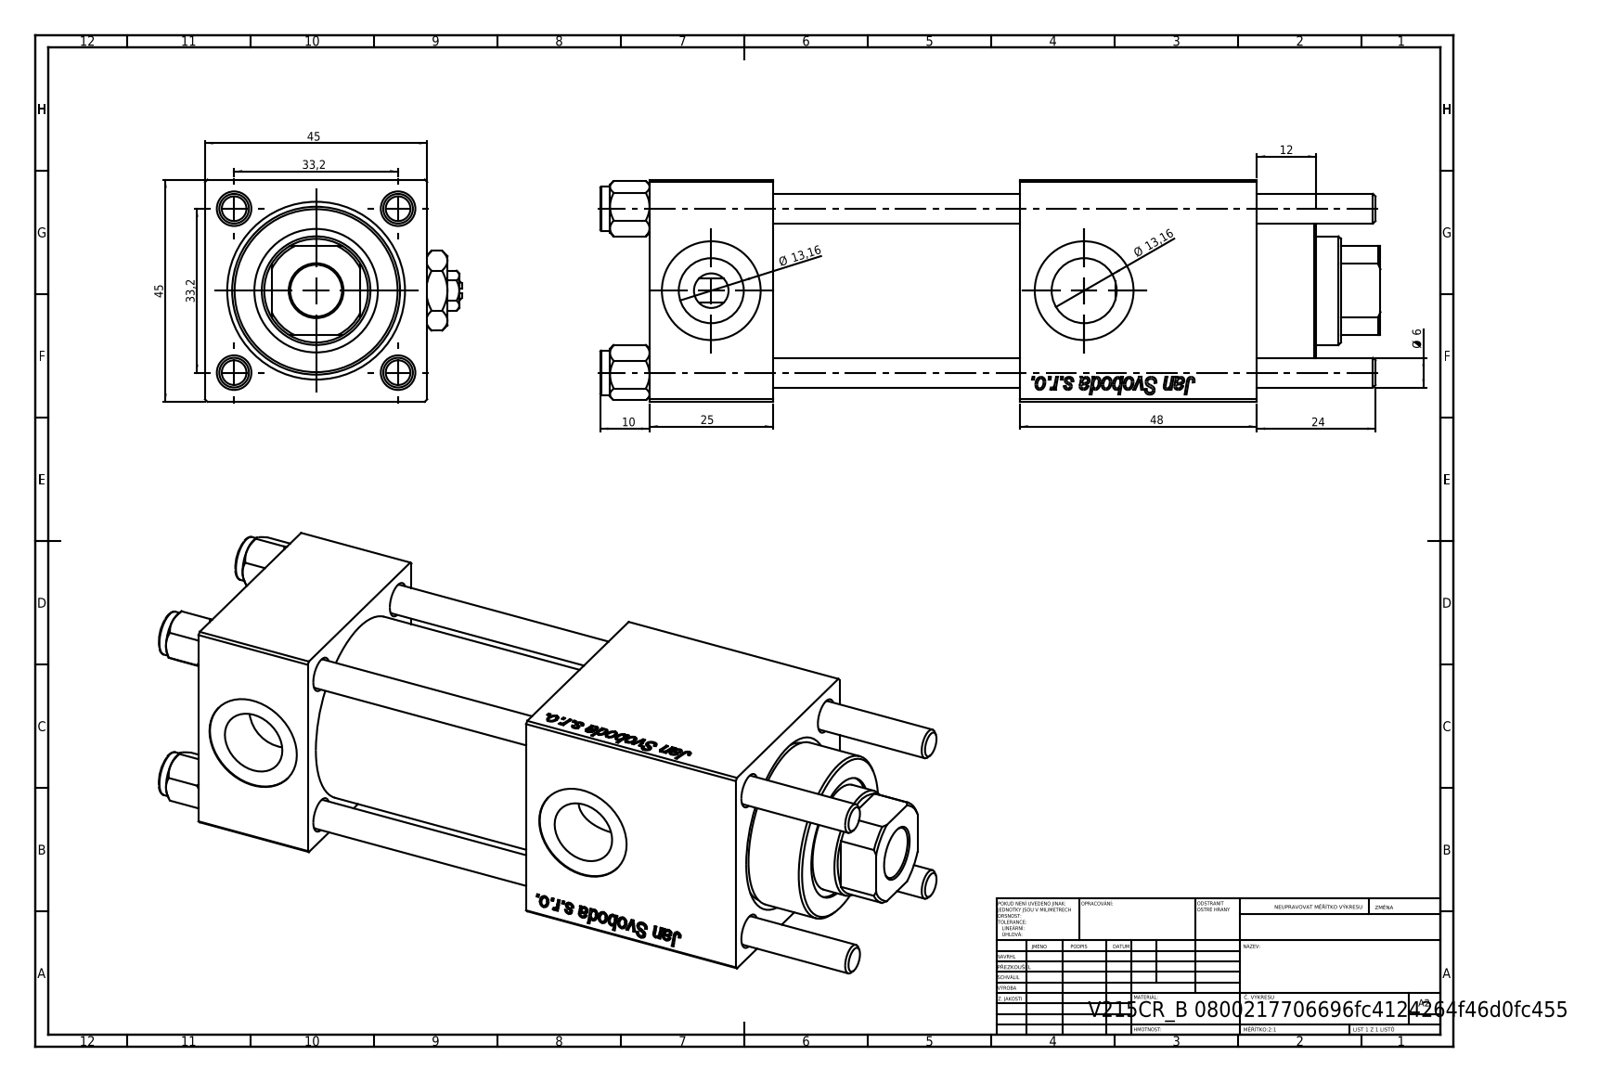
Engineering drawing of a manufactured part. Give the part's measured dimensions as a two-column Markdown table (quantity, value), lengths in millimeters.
| quantity | value |
| --- | --- |
| part name | V215CR_B-1; NUT_M5_B; V215CR_B_TYCINKA; V215CR_VCP_B (+2 more) |
| STEP written by | SolidWorks 2019 (CONFIG_CONTROL_DESIGN) |
| units | millimeters |
| bodies | 12 solids, 1208 faces (454 planar, 84 cylindrical, 670 other) |
| overall size | 158 × 52 × 45 |
| volume | 213 485 mm³ |
| surface area | 77 868 mm² |
| round holes (diameter × count) | 6 × 4, 7 × 2, 13.16 × 2, 20 × 2, 10.5 × 1, 22 × 1, 24 × 1, 25 × 1, 32 × 1, 33 × 1 |
| round bosses / shafts (diameter × count) | 9 × 4, 38 × 1, 34 × 1 |
| partial cylindrical surfaces (radius × count) | 10.5 × 1 |
| main face-to-face distances | 45, 25, 50, 123, 75, 98, 48, 94.3, 69.3, 19.3 |
| hole center spacings | 23.48, 33.2, 46.95, 75.5 |
